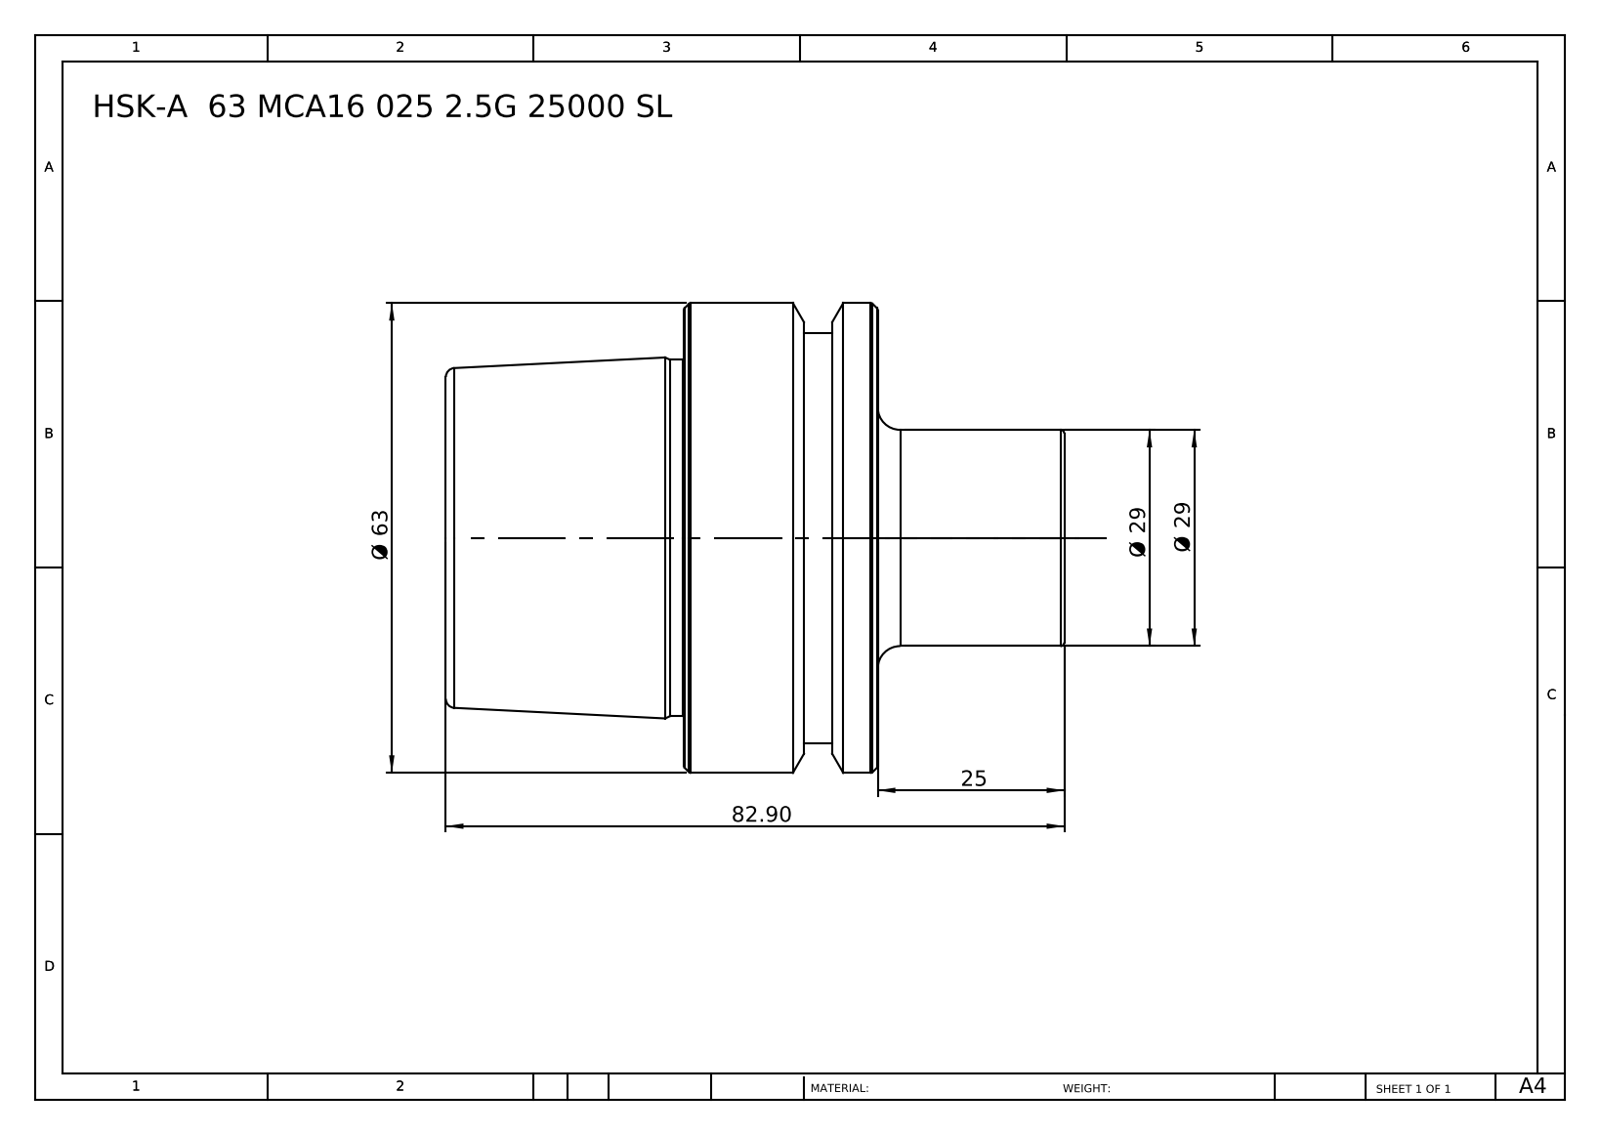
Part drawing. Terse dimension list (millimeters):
name: HSK-A 63 MCA16 025 2.5G 25000 SL
written by: SolidWorks 2014 (CONFIG_CONTROL_DESIGN)
unit: mm
bodies: 1 solid, 46 faces (6 planar, 10 cylindrical, 30 other)
size: 82.9 × 63 × 63
volume: 149 288 mm³; area: 18 794 mm²
bosses: 1× ⌀63, 1× ⌀55, 1× ⌀47.78, 1× ⌀29
face distances: 57.9, 26, 31.9, 25, 51, 82.9, 31.1, 6.1, 19.9, 51.8
